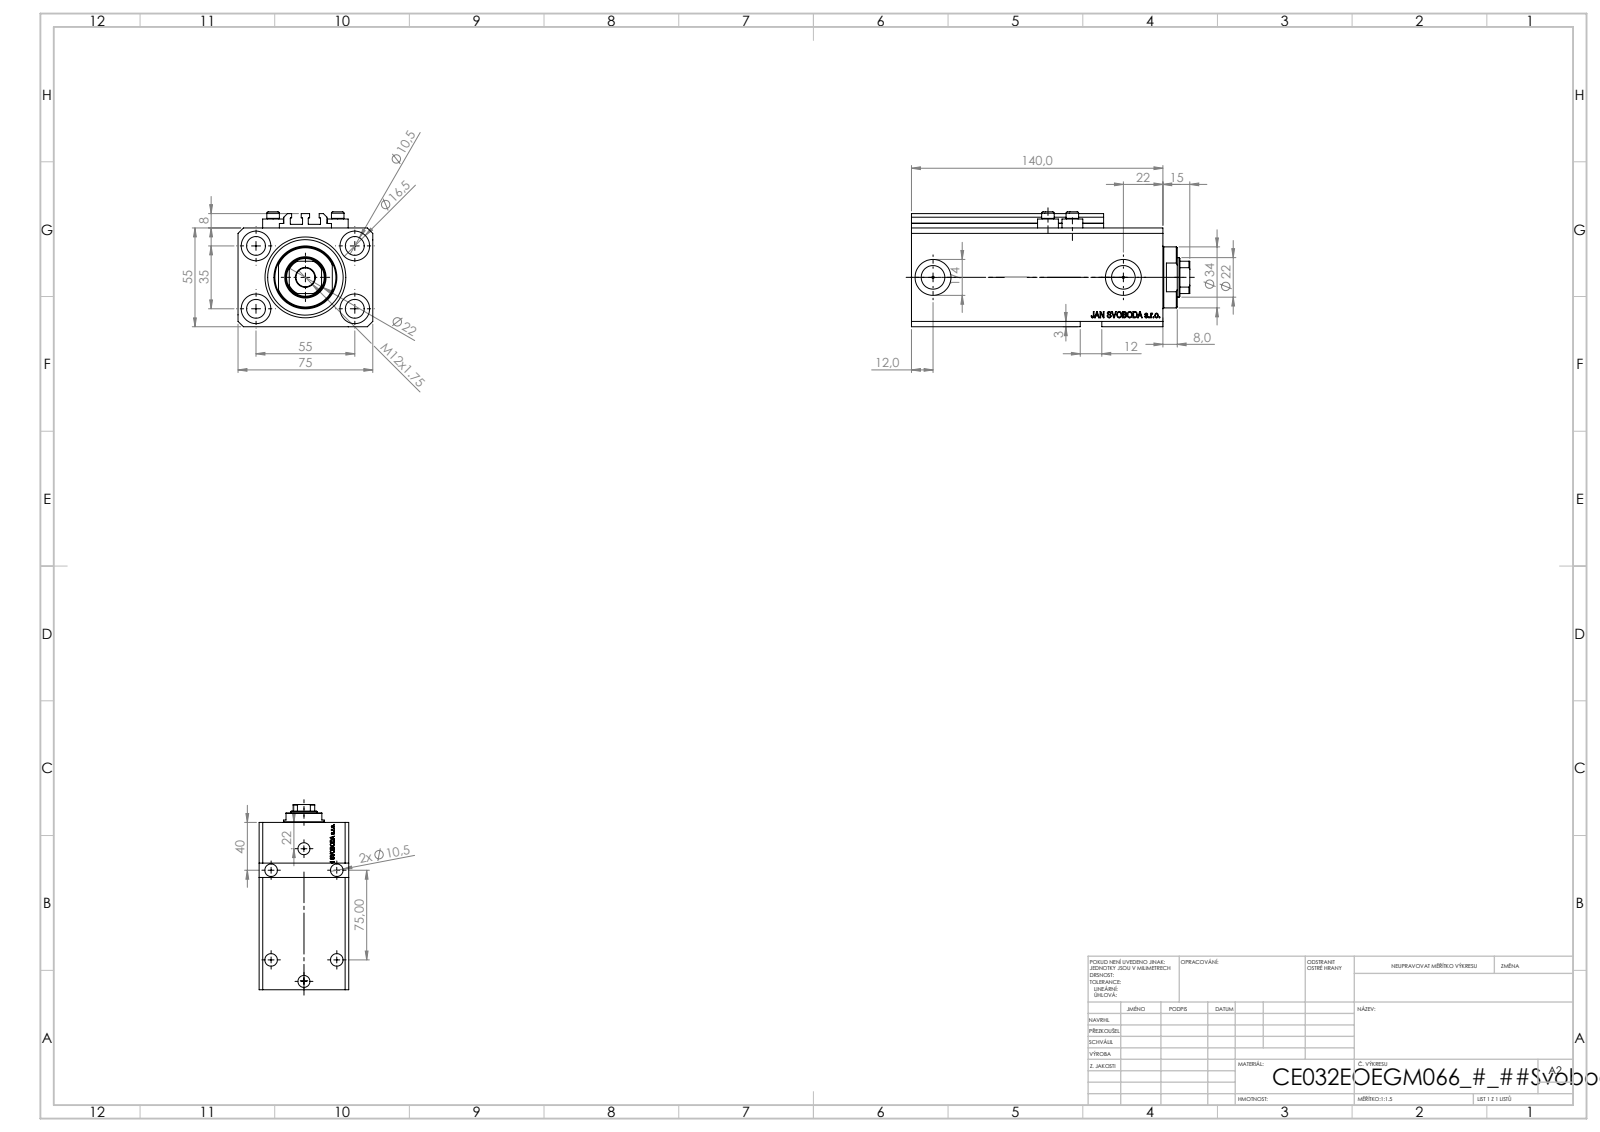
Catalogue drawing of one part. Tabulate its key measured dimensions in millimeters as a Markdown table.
| quantity | value |
| --- | --- |
| part name | V250CE_E_Body; V250CE_C_VCP; ALLEN BOLT V250CE; V250CE_VC_E |
| STEP written by | SolidWorks 2019 (CONFIG_CONTROL_DESIGN) |
| units | millimeters |
| bodies | 8 solids, 1084 faces (514 planar, 146 cylindrical, 424 other) |
| overall size | 155 × 75 × 64 |
| volume | 485 219 mm³ |
| surface area | 115 303 mm² |
| round holes (diameter × count) | 10.5 × 9, 1.25 × 4, 4 × 4, 16.5 × 4, 10 × 2, 13.16 × 2, 20 × 2, 22 × 1, 32 × 1, 45 × 1 |
| round bosses / shafts (diameter × count) | 11.6 × 4, 7 × 4, 34 × 1 |
| partial cylindrical surfaces (radius × count) | 0.2 × 10, 10.5 × 1 |
| main face-to-face distances | 55, 75, 15, 140, 125, 3, 9.9, 57, 115.1, 130.1 |
| hole center spacings | 32.6, 32.87, 55, 96.98, 13.6, 14.09, 25.81, 32.58 |
